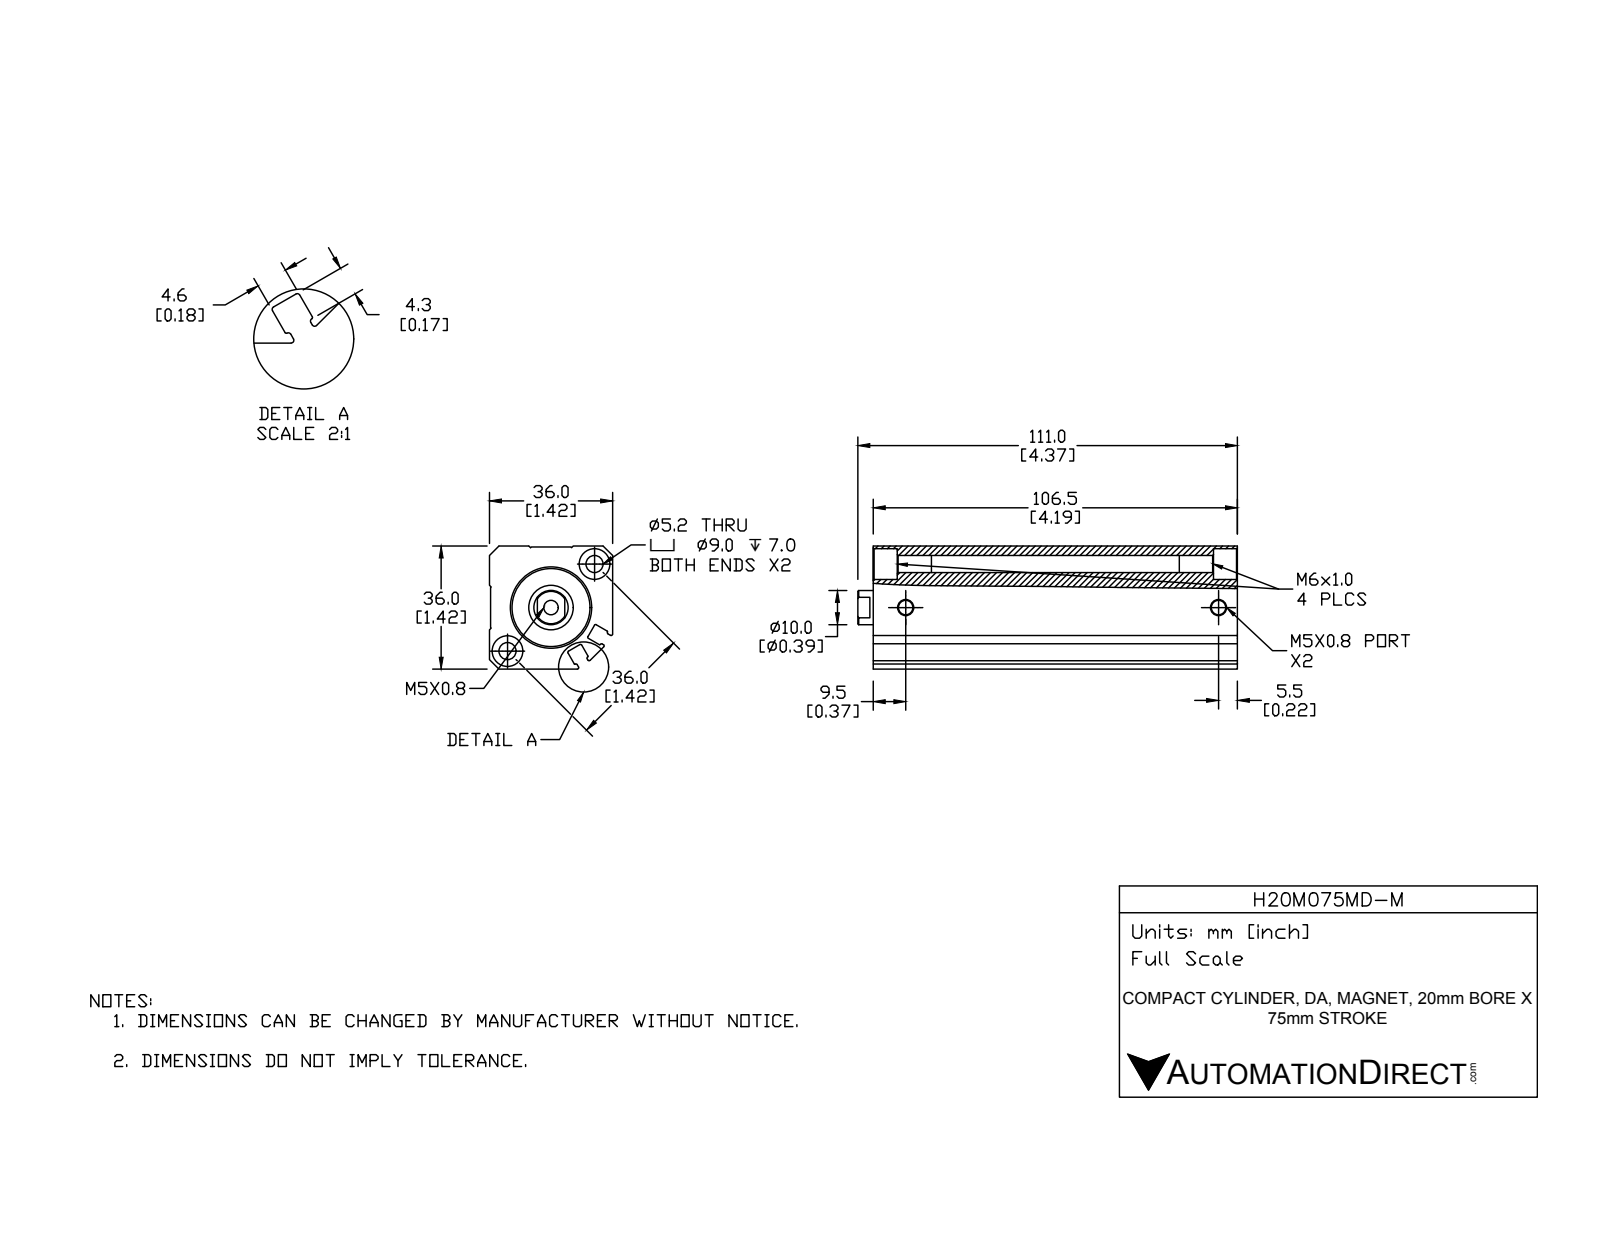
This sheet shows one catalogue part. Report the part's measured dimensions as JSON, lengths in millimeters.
{"part_name": "H20M075MD-M-PISTON; H20M075MD-M; H20M075MD-M-BODY", "step_written_by": "SolidWorks 2015 (CONFIG_CONTROL_DESIGN)", "units": "millimeters", "bodies": {"solids": 2, "faces": 141, "planar": 53, "cylindrical": 55, "other": 33}, "overall_size": [111, 36, 36], "volume_mm3": 101710, "surface_area_mm2": 34718, "round_holes": [[4.2, 3], [5, 2], [9, 2], [10, 1], [13, 1], [20, 1], [22.8, 1]], "round_bosses_or_shafts": [[11, 1]], "partial_cylinders_radius": [[0.4, 12], [0.2, 4]], "face_to_face_distances": [36, 35.7, 4, 4.6, 106.5, 102.5, 2.6, 46.98, 1.4, 105.1], "hole_center_spacings": [18, 36.01, 91.5]}
